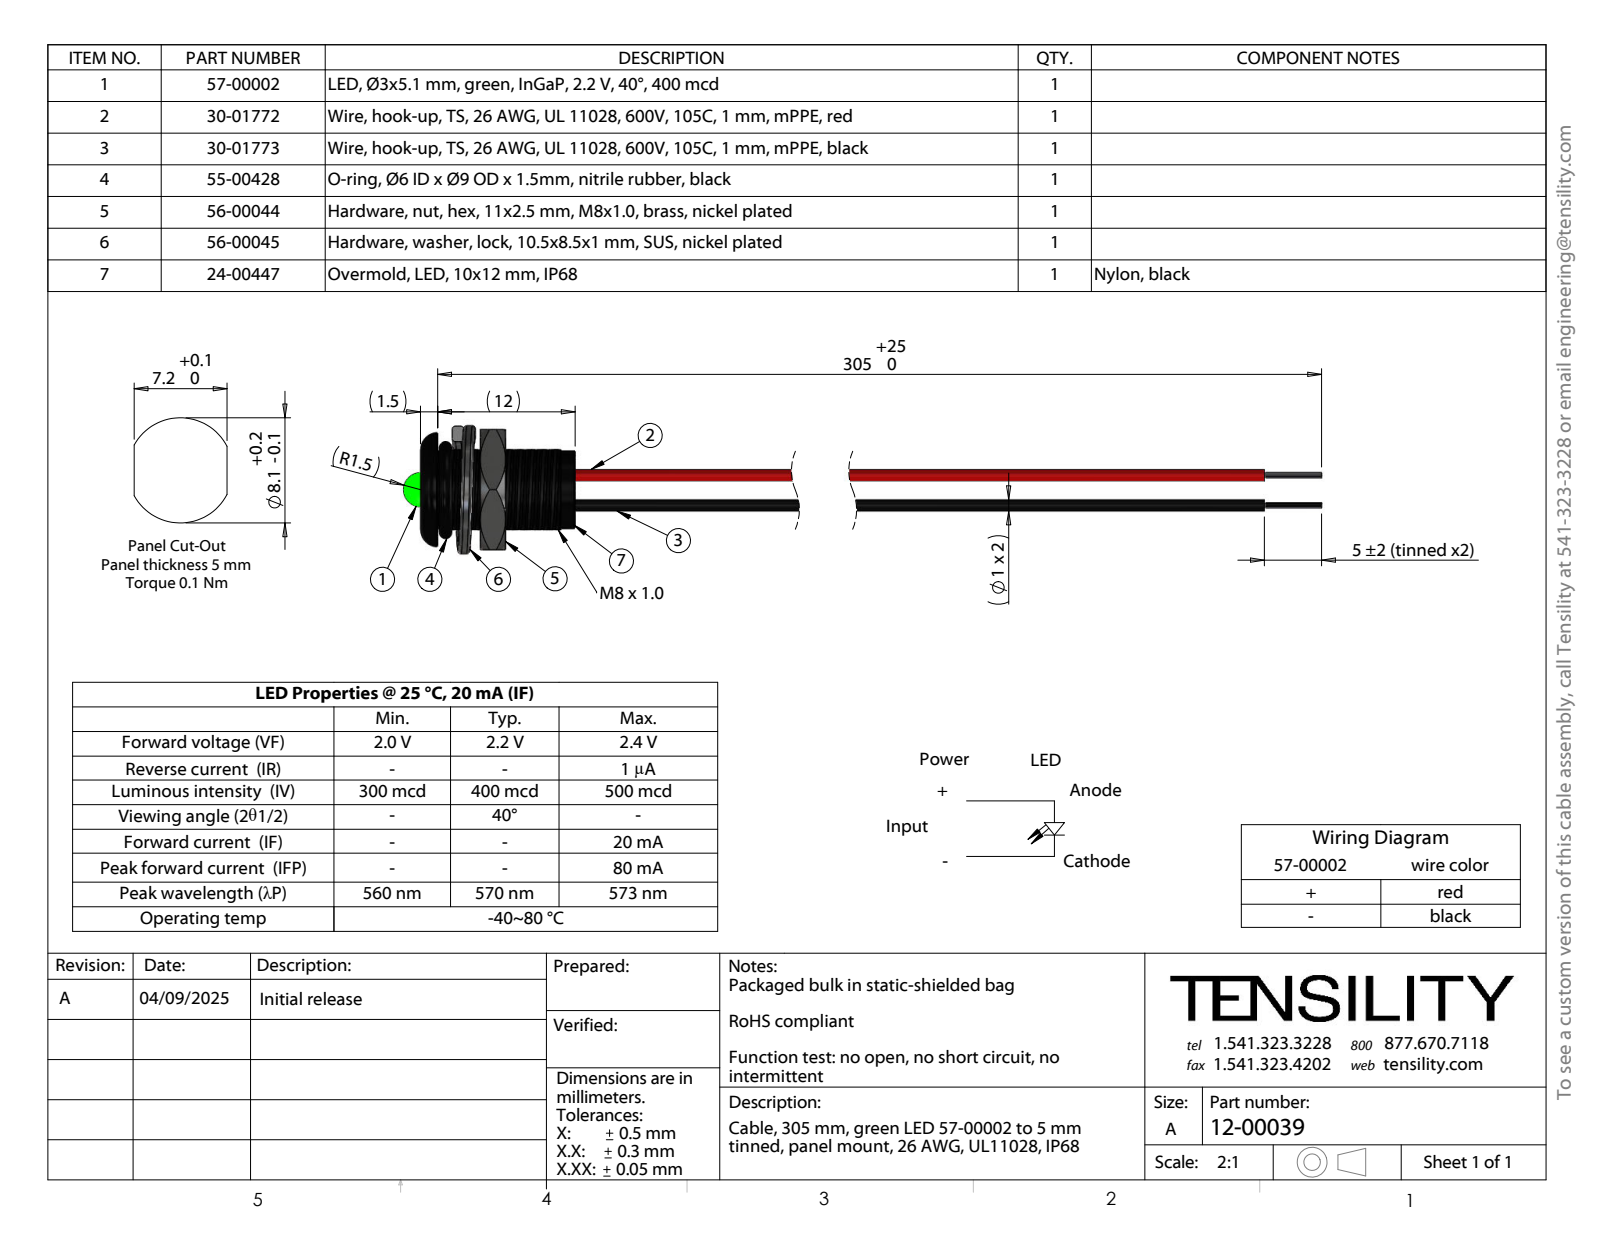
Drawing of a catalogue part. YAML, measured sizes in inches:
part_name: "24-00447; 12-00039; 30-01772_stripped and tinned; 56-00045_Split washer (+4 more)"
step_written_by: "SolidWorks 2021 (CONFIG_CONTROL_DESIGN)"
units: inches
bodies: {solids: 57, faces: 555, planar: 186, cylindrical: 246, other: 123}
overall_size: [6.693, 0.477, 0.441]
volume: 0.061
surface_area: 9.157
round_holes:
  - {diameter: 0.039, count: 2}
round_bosses_or_shafts:
  - {diameter: 0.039, count: 2}
  - {diameter: 0.02, count: 2}
  - {diameter: 0.268, count: 1}
  - {diameter: 0.118, count: 1}
partial_cylinders:
  - {radius: 0.137, count: 1}
  - {radius: 0.157, count: 1}
face_to_face_distances: [0.059, 0.531, 0.472, 0.413, 0.205, 0.146, 0.326, 0.292, 0.233, 0.087]
hole_center_spacings: [0.014, 0.015, 0.013, 0.098, 0.099, 0.096, 0.096, 0.101]
